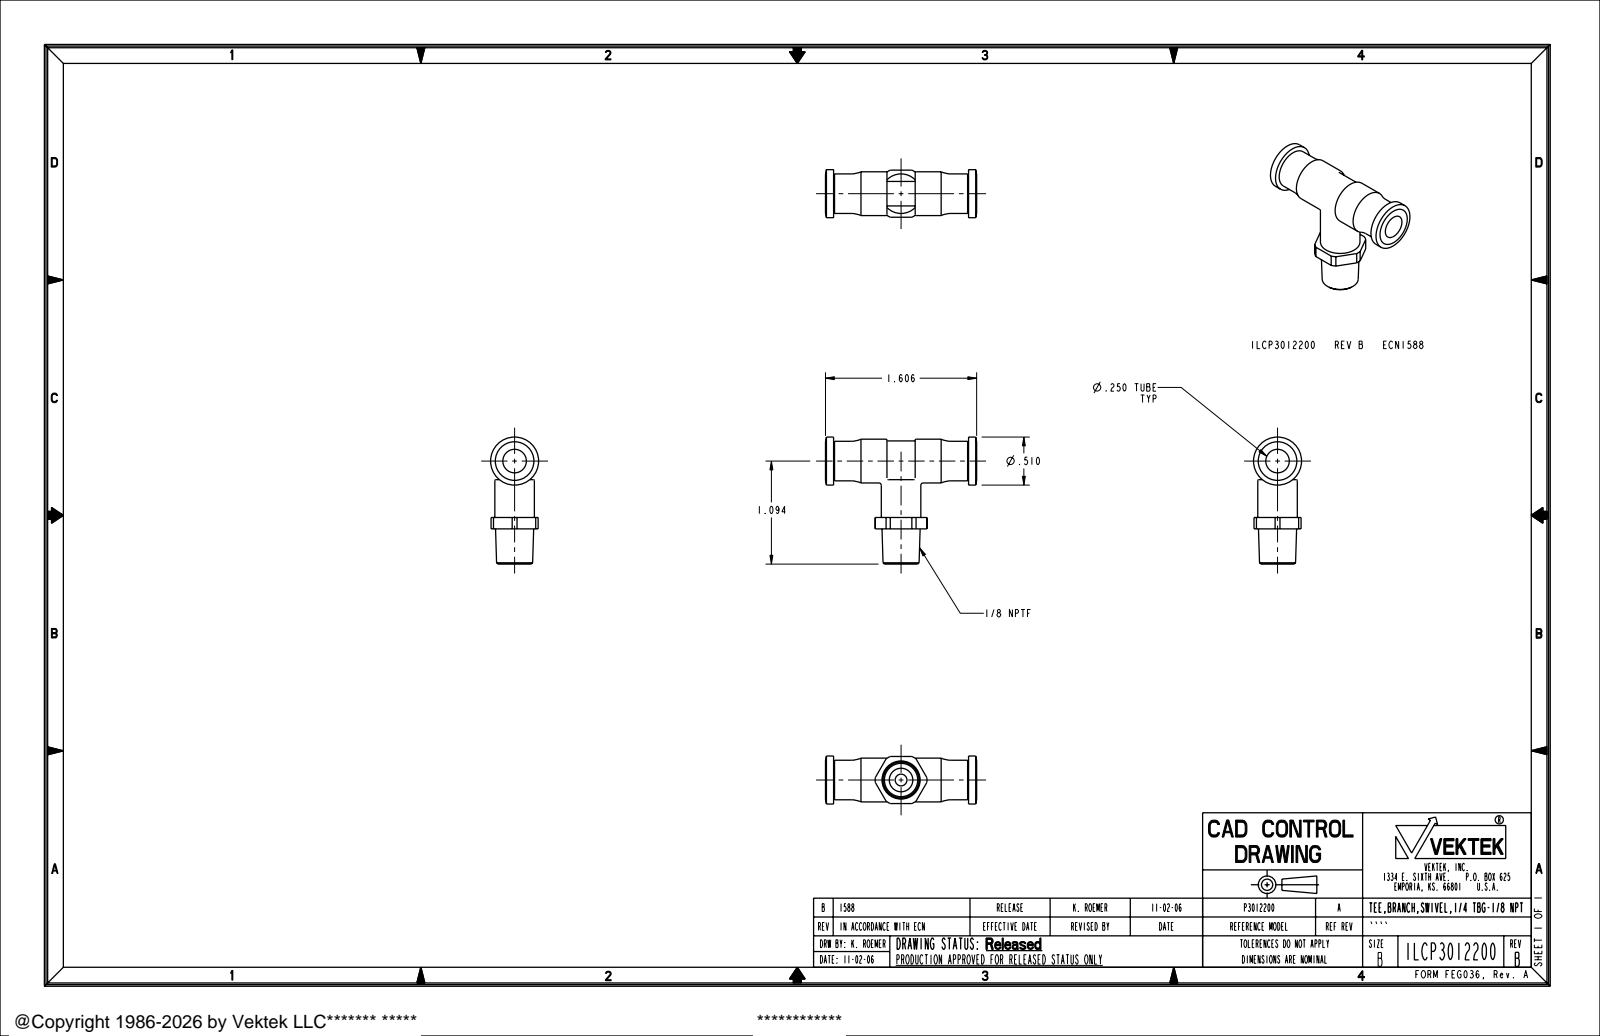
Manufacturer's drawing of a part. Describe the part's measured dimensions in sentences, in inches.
The part is named "ILCP3012200". Its 3-D file was written by "PRO/ENGINEER BY PARAMETRIC TECHNOLOGY CORPORATION, 2005180 (AUTOMOTIVE_DESIGN_CC2)". It is 1 solid with 119 faces: 22 planar, 43 cylindrical and 54 other. Overall it measures 1.606 by 1.349 by 0.51 inches. Its volume is 0.252 cubic inches and its surface area 6.335 square inches. Round holes: 2 of diameter 0.25, 1 of diameter 0.125. Round bosses or shafts: 2 of diameter 0.42, 1 of diameter 0.51, 1 of diameter 0.465, 1 of diameter 0.271. Partial cylindrical surfaces (rounded edges, fillets, slot ends): 6 of radius 0.005, 2 of radius 0.015, 2 of radius 0.02, 1 of radius 0.214, 1 of radius 0.275. The main face-to-face distances are 0.086, 1.52, 0.096, 1.51, 1.424, 1.434, 0.26, 0.653, 0.953, 0.567.
